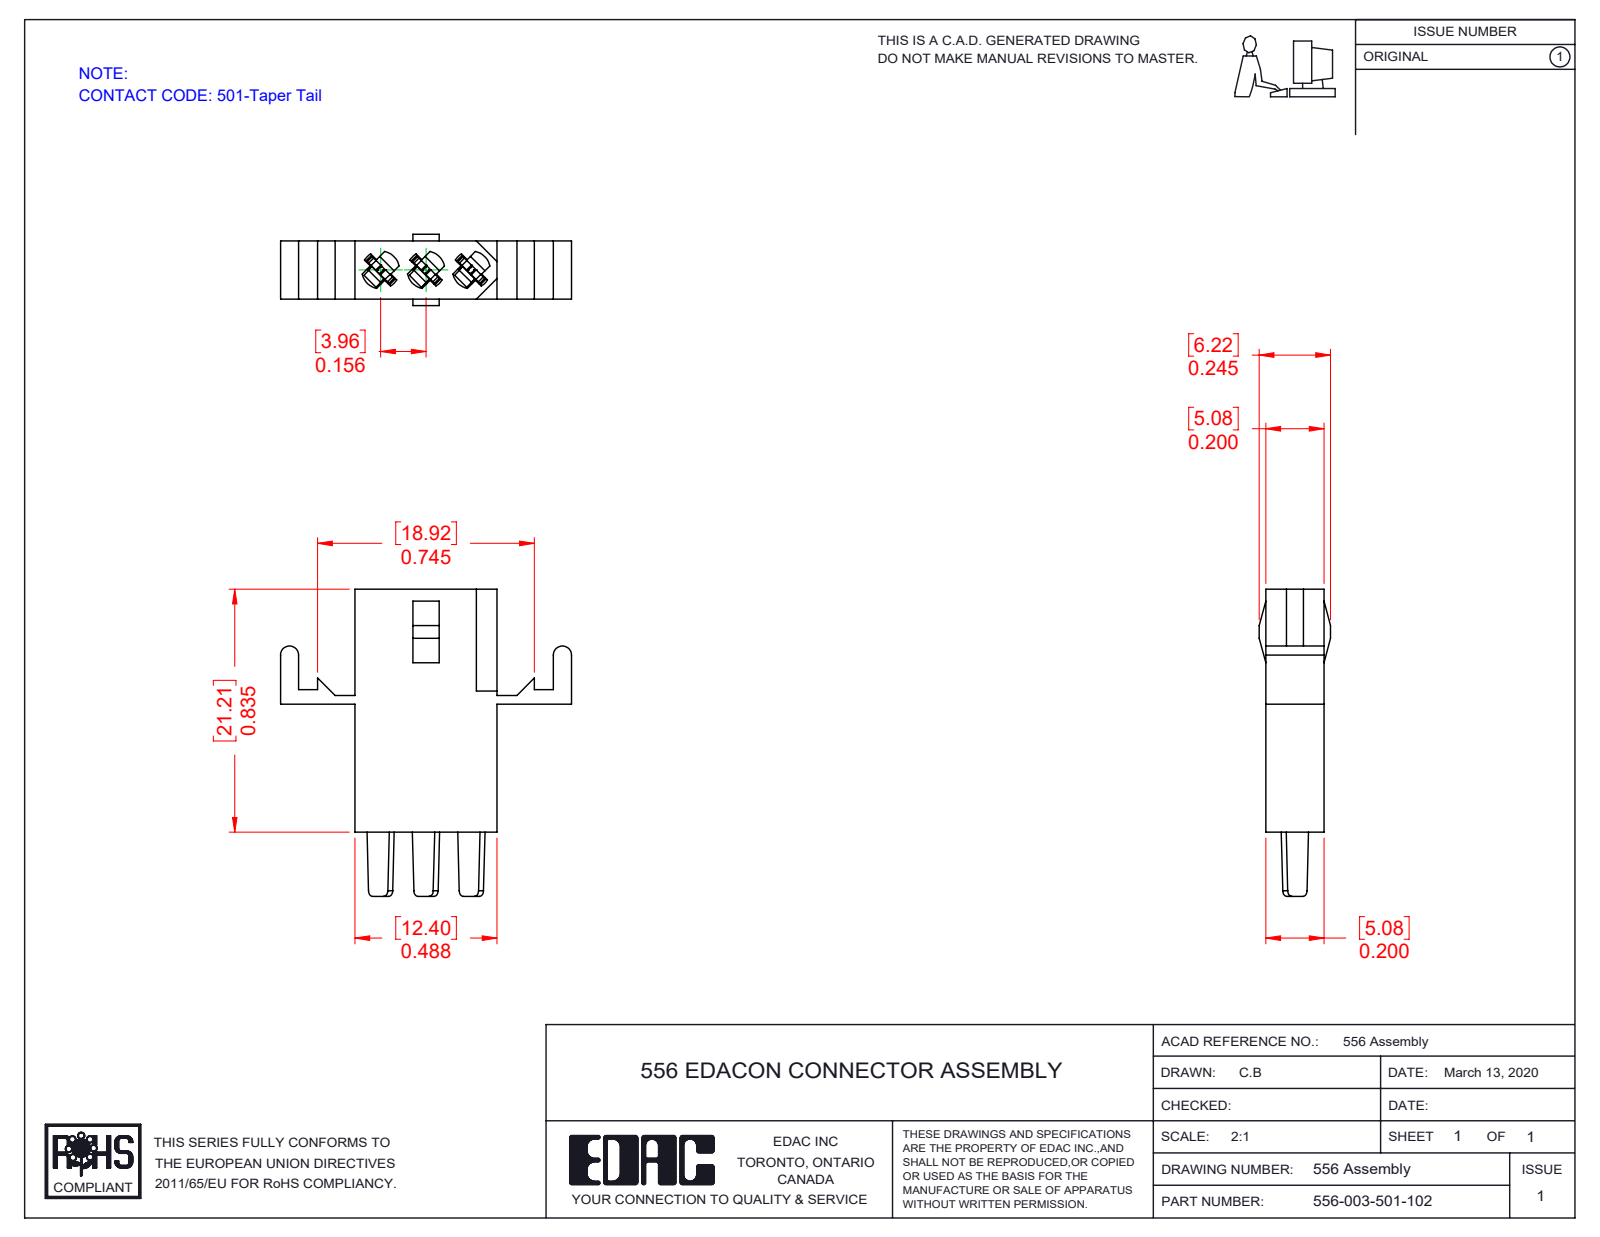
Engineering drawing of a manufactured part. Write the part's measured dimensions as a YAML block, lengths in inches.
part_name: "516-292-001_501 Contact; 556-210-001_556-003-000-102; 556-003-501-102"
step_written_by: "SolidWorks 2016 (CONFIG_CONTROL_DESIGN)"
units: inches
bodies: {solids: 4, faces: 332, planar: 213, cylindrical: 95, other: 24}
overall_size: [1.056, 1, 0.245]
volume: 0.068
surface_area: 3.705
round_holes:
  - {diameter: 0.05, count: 3}
  - {diameter: 0.132, count: 3}
partial_cylinders:
  - {radius: 0.012, count: 12}
  - {radius: 0.022, count: 12}
  - {radius: 0.007, count: 6}
  - {radius: 0.008, count: 6}
  - {radius: 0.016, count: 6}
  - {radius: 0.02, count: 6}
  - {radius: 0.08, count: 6}
  - {radius: 0.065, count: 3}
face_to_face_distances: [0.11, 0.2, 0.22, 0.024, 0.134, 0.027, 0.03, 0.07, 0.488, 0.111]
hole_center_spacings: [0.11, 0.156, 0.22, 0.312]
